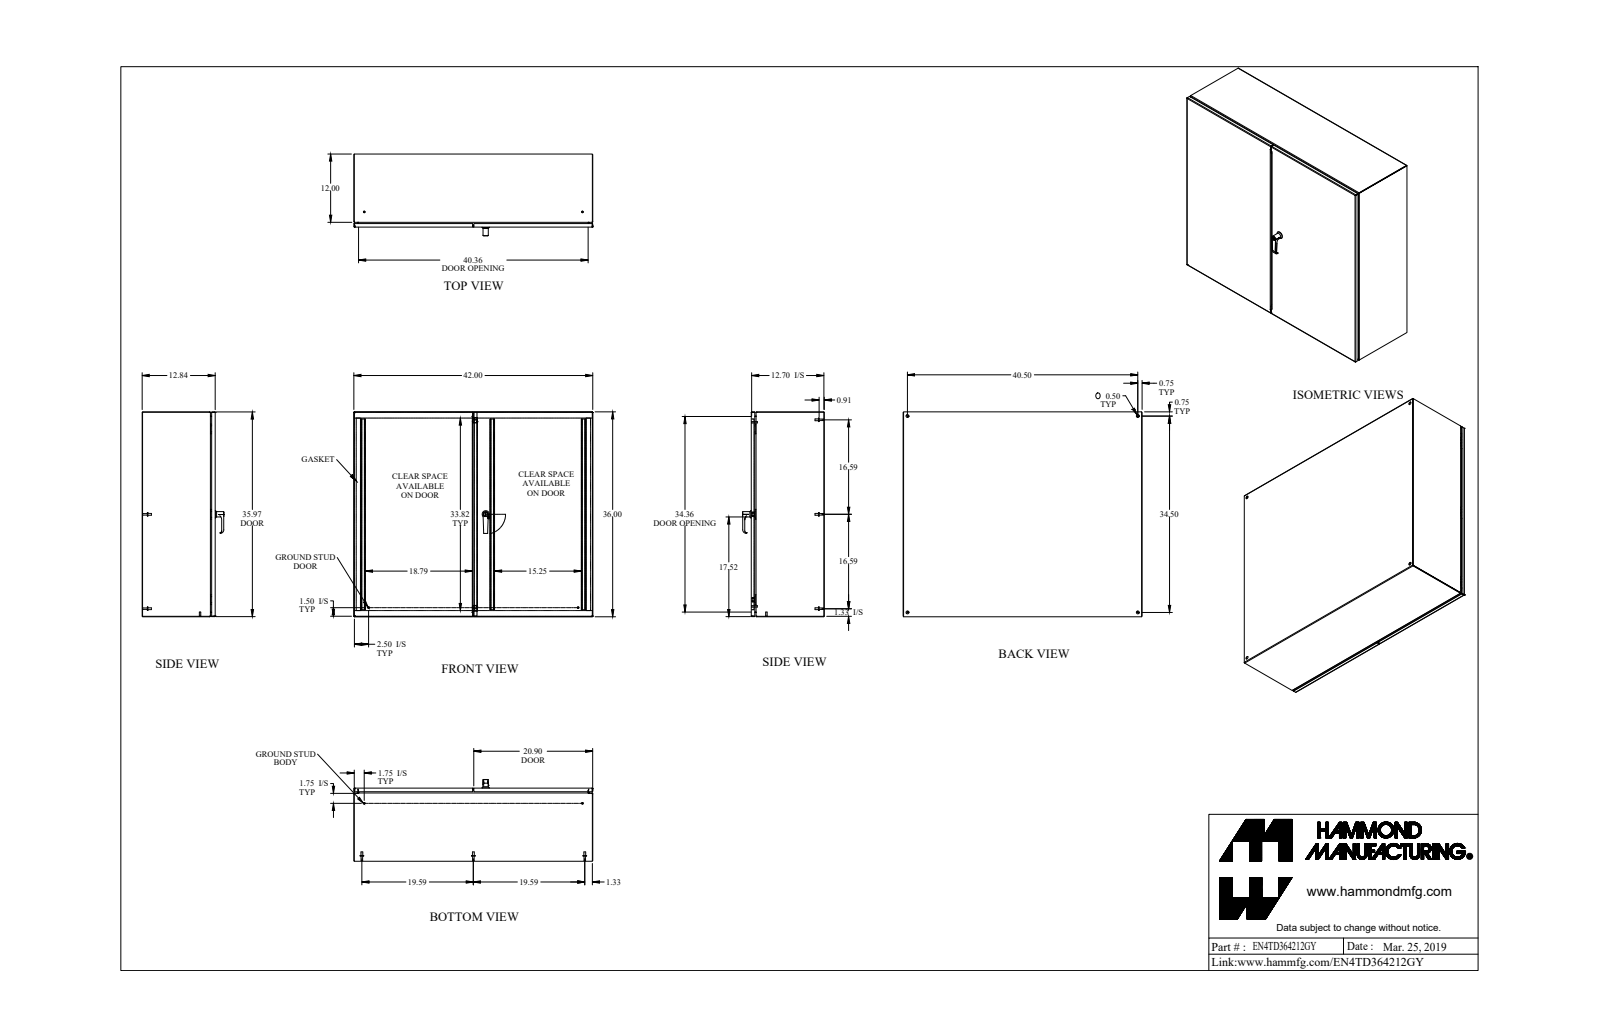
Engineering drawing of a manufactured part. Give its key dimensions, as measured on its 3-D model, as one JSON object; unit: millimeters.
{"part_name": "EN4TD364212GY", "step_written_by": "SolidWorks 2018 (AUTOMOTIVE_DESIGN)", "units": "millimeters", "bodies": {"solids": 87, "faces": 2175, "planar": 967, "cylindrical": 802, "other": 406}, "overall_size": [1066.8, 914.4, 365], "volume_mm3": 7122000, "surface_area_mm2": 7413000, "round_holes": [[5, 5], [4.5, 4], [12.7, 4], [6.1, 3], [6.1, 3], [6.7, 3], [4.4, 2], [6.4, 2], [6.5, 2], [6.6, 2], [6.7, 2], [8, 2]], "round_bosses_or_shafts": [[6.4, 11], [8, 10], [6.9, 8], [15.9, 6], [13, 4], [9.5, 4], [7.1, 4], [4, 4]], "partial_cylinders_radius": [[0.9, 26], [2.7, 26], [1.6, 25], [2.4, 20], [1.1, 18], [2.1, 18], [0.5, 16], [0.4, 15]], "face_to_face_distances": [1.8, 324.4, 322.5, 326.2, 912.6, 1065, 910.7, 914.4, 1063.1, 1066.8], "hole_center_spacings": [20, 578, 634.8, 718.5, 876.3, 1028.7, 1351.3, 20]}
